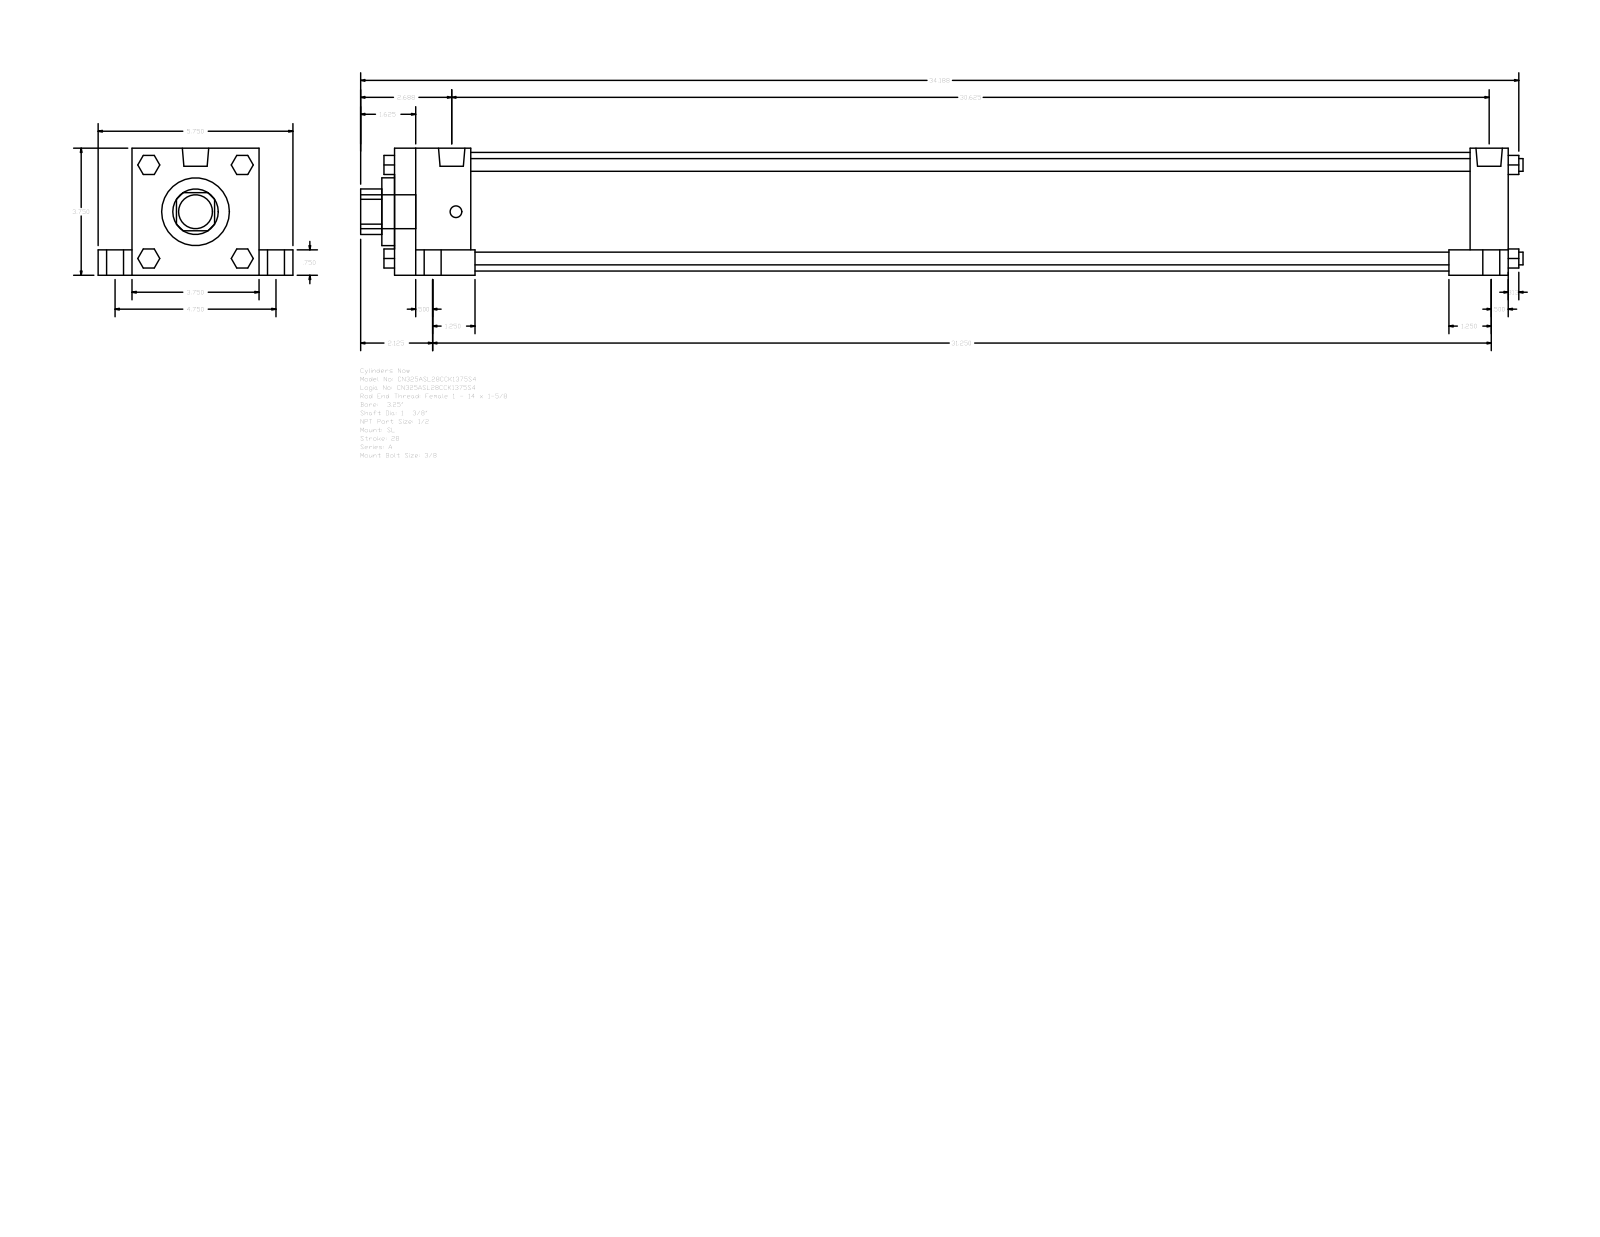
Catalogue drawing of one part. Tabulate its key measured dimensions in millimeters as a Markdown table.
| quantity | value |
| --- | --- |
| part name | A_SL__0325_1.375 |
| STEP written by | GSSL Pune (CONFIG_CONTROL_DESIGN) |
| units | millimeters |
| bodies | 0 solids, 150 faces (114 planar, 36 cylindrical, 0 other) |
| overall size | 871.54 × 146.05 × 95.25 |
| round holes (diameter × count) | 34.92 × 1, 50.8 × 1, 88.9 × 1 |
| round bosses / shafts (diameter × count) | 19.05 × 4, 12.7 × 4, 9.53 × 4, 8.73 × 4, 19.77 × 2, 25.4 × 1 |
| partial cylindrical surfaces (radius × count) | 17.06 × 1 |
| main face-to-face distances | 95.24, 835.02, 25.41, 120.65, 19.05, 76.19, 15.87, 28.57, 57.15, 806.45 |
